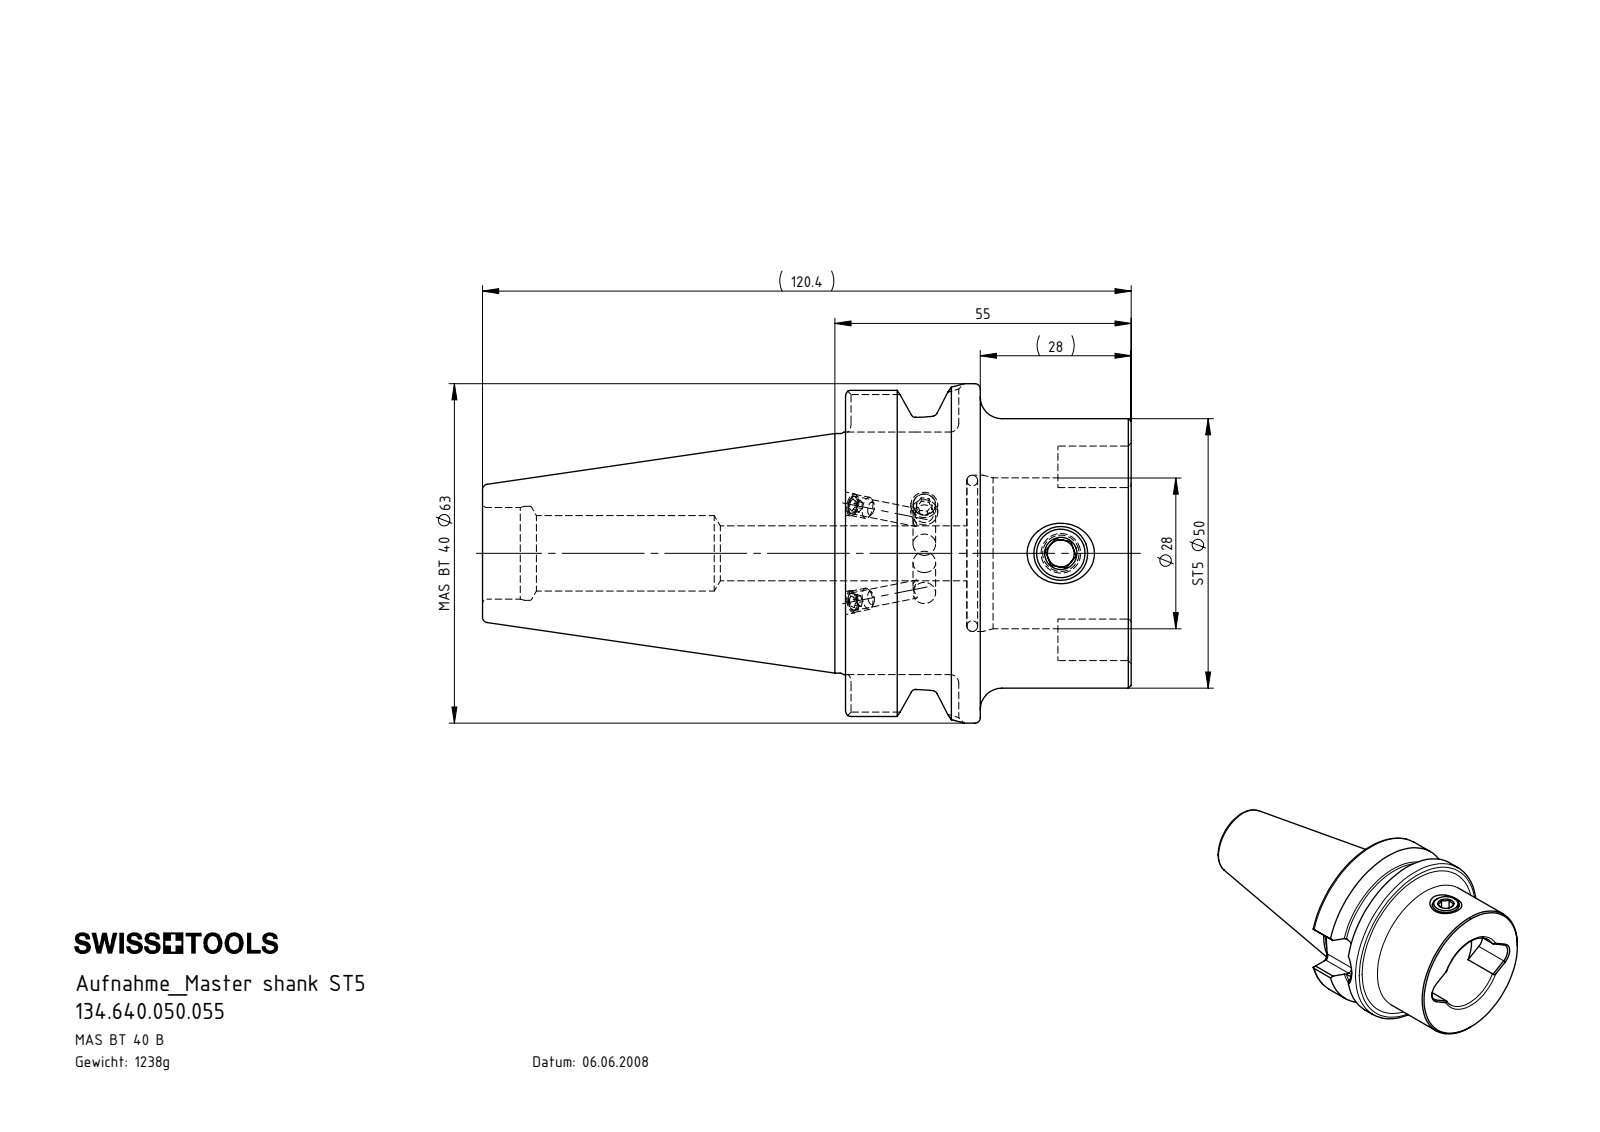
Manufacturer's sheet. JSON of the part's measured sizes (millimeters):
{"part_name": "ST5-ER1.001.012_A; BB4-ST5.K01.055; DIN 3771 - 25x2; ISO 4026 - M4 x 4_PreviewCfg (+2 more)", "step_written_by": "SolidWorks 2015 (CONFIG_CONTROL_DESIGN)", "units": "millimeters", "bodies": {"solids": 6, "faces": 204, "planar": 63, "cylindrical": 59, "other": 82}, "overall_size": [120.4, 63, 63], "volume_mm3": 157989, "surface_area_mm2": 30915, "round_holes": [[4.2, 3], [3.3, 2], [9, 1], [10.2, 1], [14, 1], [17, 1], [17.45, 1], [28, 1], [29, 1]], "round_bosses_or_shafts": [[4, 2], [63, 1], [53, 1], [50, 1], [44.45, 1], [10, 1], [5, 1]], "partial_cylinders_radius": [[1.6, 8], [4.2, 2], [8.05, 1]], "face_to_face_distances": [53, 22.5, 30.5, 25, 2.5, 28, 45, 24.1, 67.4, 89.9]}
